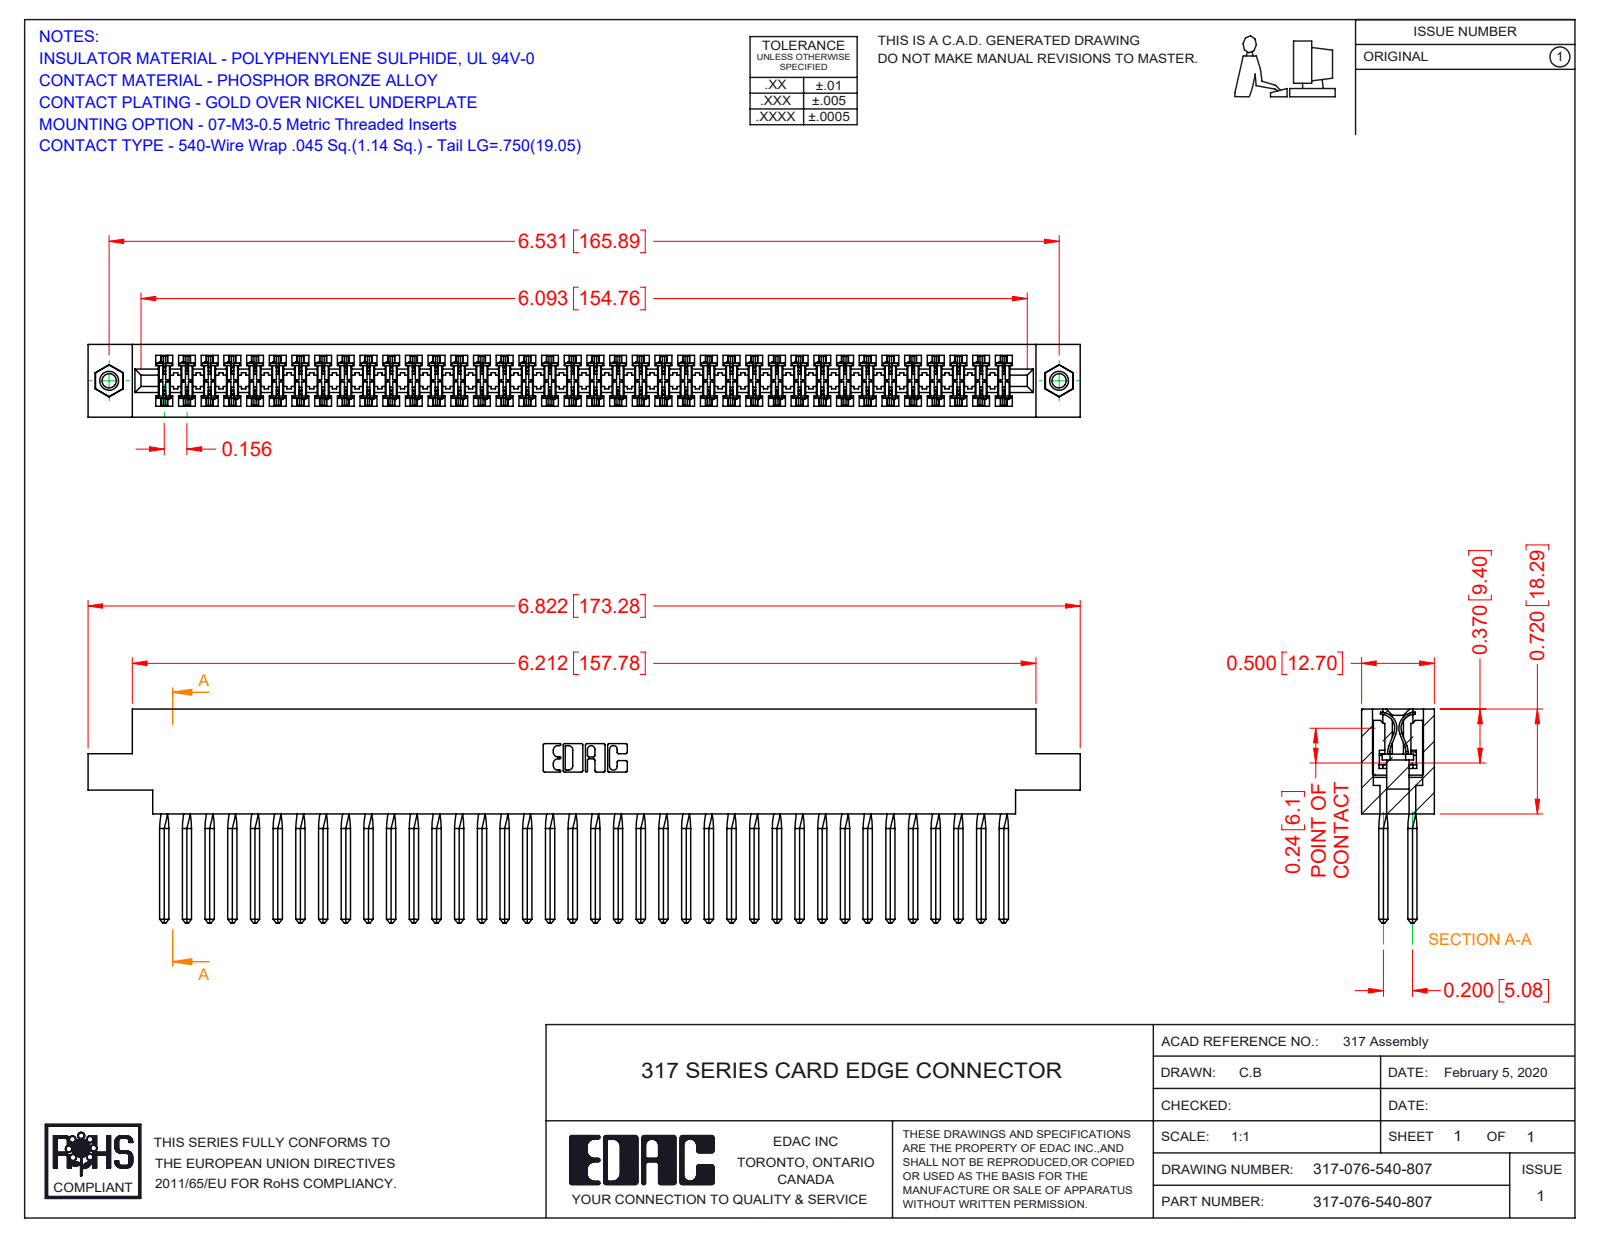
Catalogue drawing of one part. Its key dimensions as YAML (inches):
part_name: "317-076-540-807; 317-290-001_540; 345-250-001_345-250-005-103; 317 Part_.156 Dia - TI"
step_written_by: "SolidWorks 2016 (CONFIG_CONTROL_DESIGN)"
units: inches
bodies: {solids: 79, faces: 6926, planar: 5638, cylindrical: 968, other: 320}
overall_size: [6.822, 1.47, 0.5]
volume: 1.766
surface_area: 66.68
round_holes:
  - {diameter: 0.098, count: 2}
  - {diameter: 0.125, count: 2}
  - {diameter: 0.156, count: 2}
round_bosses_or_shafts:
  - {diameter: 0.155, count: 2}
partial_cylinders:
  - {radius: 0.015, count: 152}
  - {radius: 0.01, count: 22}
  - {radius: 0.007, count: 6}
  - {radius: 0.031, count: 6}
  - {radius: 0.026, count: 3}
  - {radius: 0.095, count: 2}
  - {radius: 0.1, count: 2}
  - {radius: 0.11, count: 2}
face_to_face_distances: [0.5, 0.075, 0.425, 0.35, 0.195, 0.094, 0.11, 0.2, 0.115, 0.131]
hole_center_spacings: [6.531]
